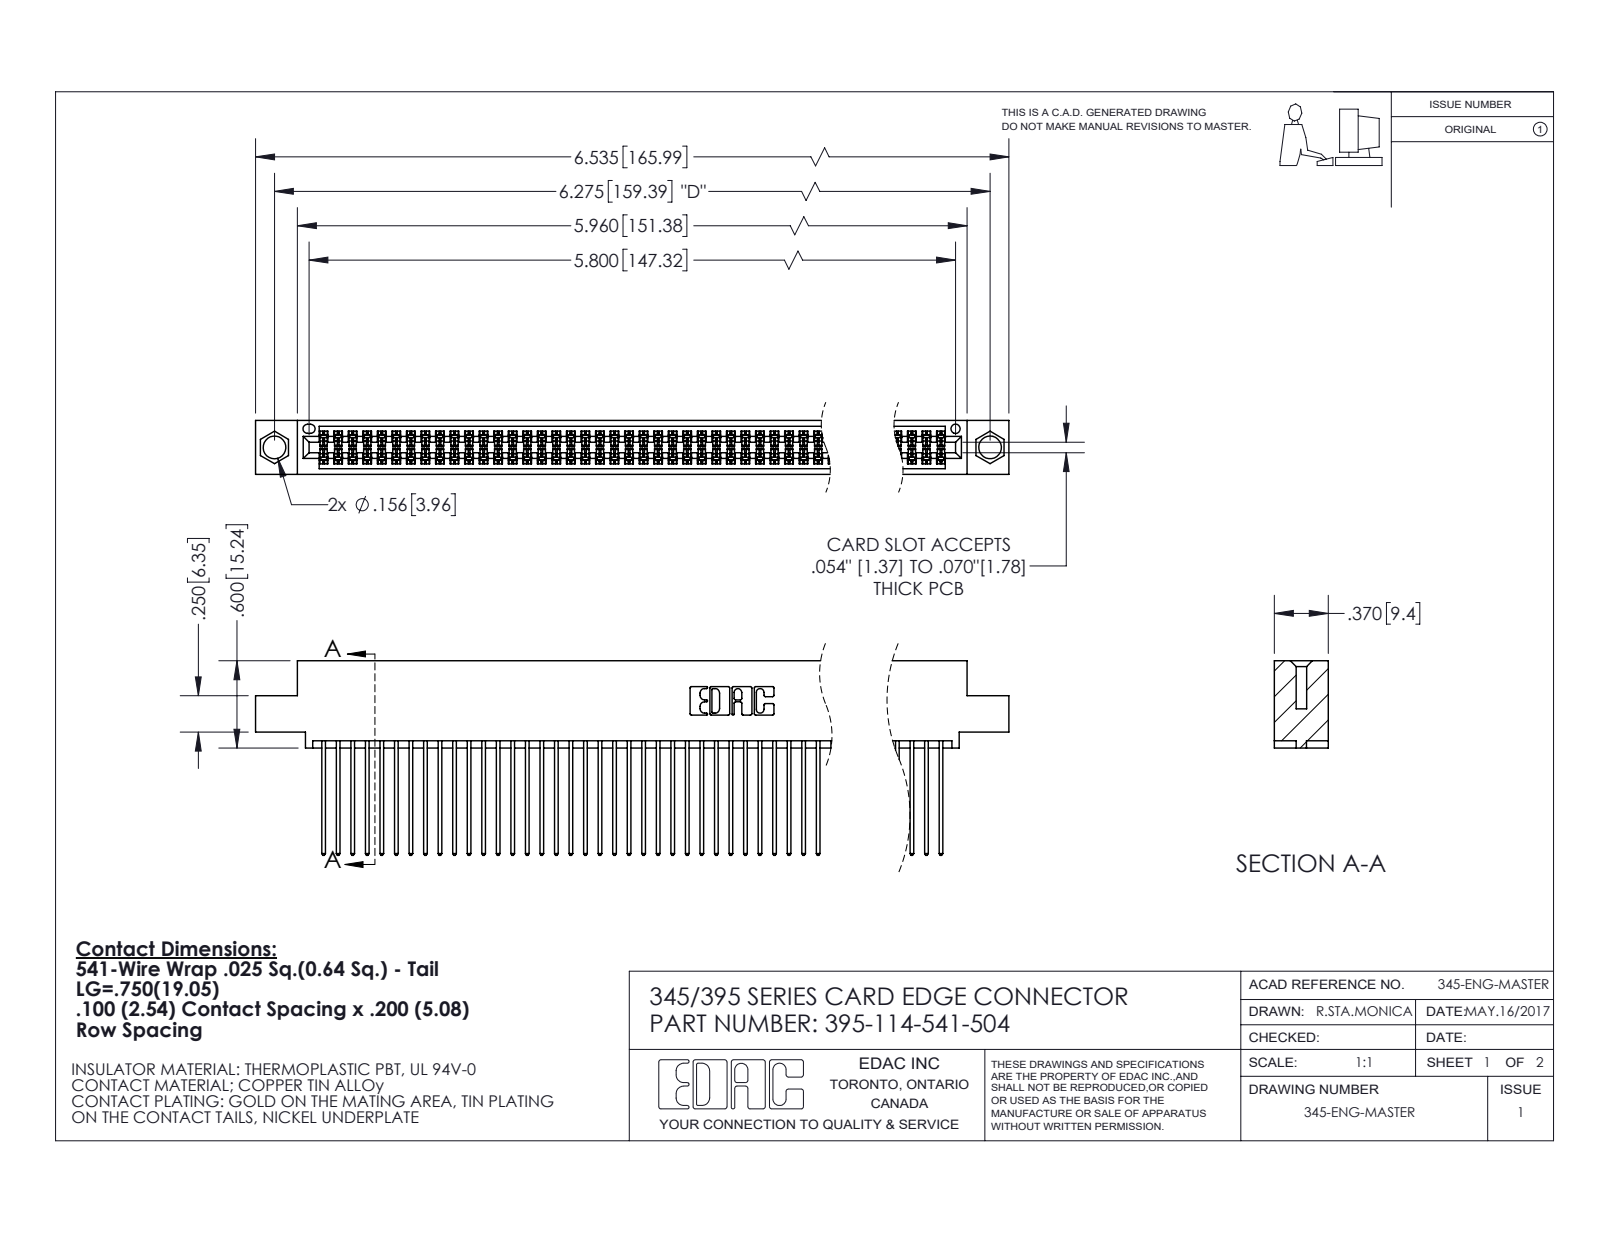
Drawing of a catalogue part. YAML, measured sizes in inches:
part_name: "345-292-001_345-293-141; 395-114-541-504; 345 Part_0.110 Offset - 0.156 Dia-TI"
step_written_by: "SolidWorks 2020 (CONFIG_CONTROL_DESIGN)"
units: inches
bodies: {solids: 115, faces: 5844, planar: 3860, cylindrical: 1984, other: 0}
overall_size: [6.535, 1.337, 0.37]
volume: 1.021
surface_area: 43.48
round_holes:
  - {diameter: 0.156, count: 2}
  - {diameter: 0.064, count: 1}
partial_cylinders:
  - {radius: 0.006, count: 171}
  - {radius: 0.01, count: 114}
  - {radius: 0.01, count: 22}
  - {radius: 0.007, count: 6}
  - {radius: 0.031, count: 6}
  - {radius: 0.026, count: 3}
  - {radius: 0.014, count: 2}
  - {radius: 0.019, count: 2}
face_to_face_distances: [0.298, 0.072, 0.2, 0.098, 0.272, 0.025, 0.225, 0.37, 0.175, 0.149]
hole_center_spacings: [0.27, 6.039, 6.275]
